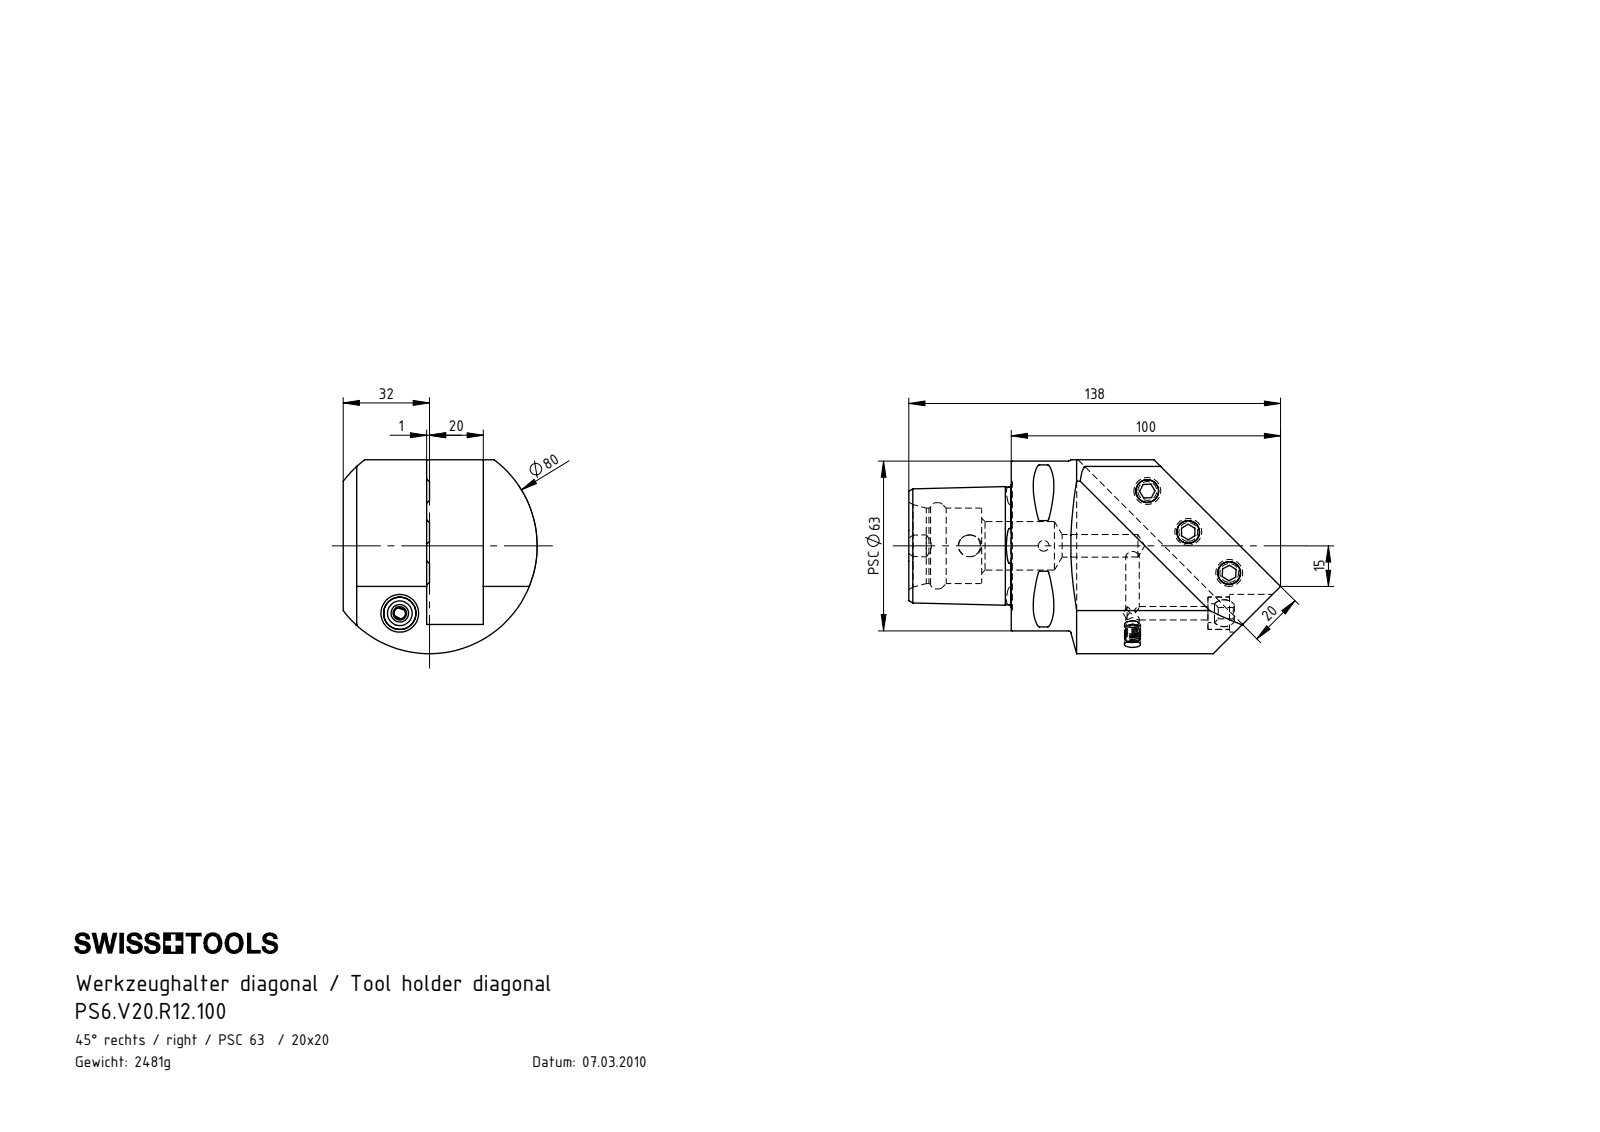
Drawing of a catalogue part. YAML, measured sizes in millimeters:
part_name: "PS6-V20.R12.100; KVT_MB_600_060; ISO 4026 - M10 x 25; KU1-U12.001.010 (+3 more)"
step_written_by: "SolidWorks 2012 (CONFIG_CONTROL_DESIGN)"
units: millimeters
bodies: {solids: 8, faces: 257, planar: 62, cylindrical: 67, other: 128}
overall_size: [138, 72, 72]
volume: 316292
surface_area: 47526
round_holes:
  - {diameter: 5, count: 3}
  - {diameter: 8.5, count: 3}
  - {diameter: 4, count: 1}
  - {diameter: 4.2, count: 1}
  - {diameter: 6, count: 1}
  - {diameter: 7, count: 1}
  - {diameter: 8.1, count: 1}
  - {diameter: 8.4, count: 1}
  - {diameter: 12, count: 1}
  - {diameter: 14, count: 1}
  - {diameter: 18, count: 1}
  - {diameter: 28, count: 1}
round_bosses_or_shafts:
  - {diameter: 10, count: 3}
  - {diameter: 63, count: 1}
  - {diameter: 6, count: 1}
partial_cylinders:
  - {radius: 0.5, count: 8}
  - {radius: 6, count: 1}
  - {radius: 40, count: 1}
face_to_face_distances: [20, 5, 21, 47, 26, 52, 31, 38, 27, 24.88]
hole_center_spacings: [21.5, 21.51, 27.31, 27.5, 43.01, 43.55, 53.96, 69.07]
